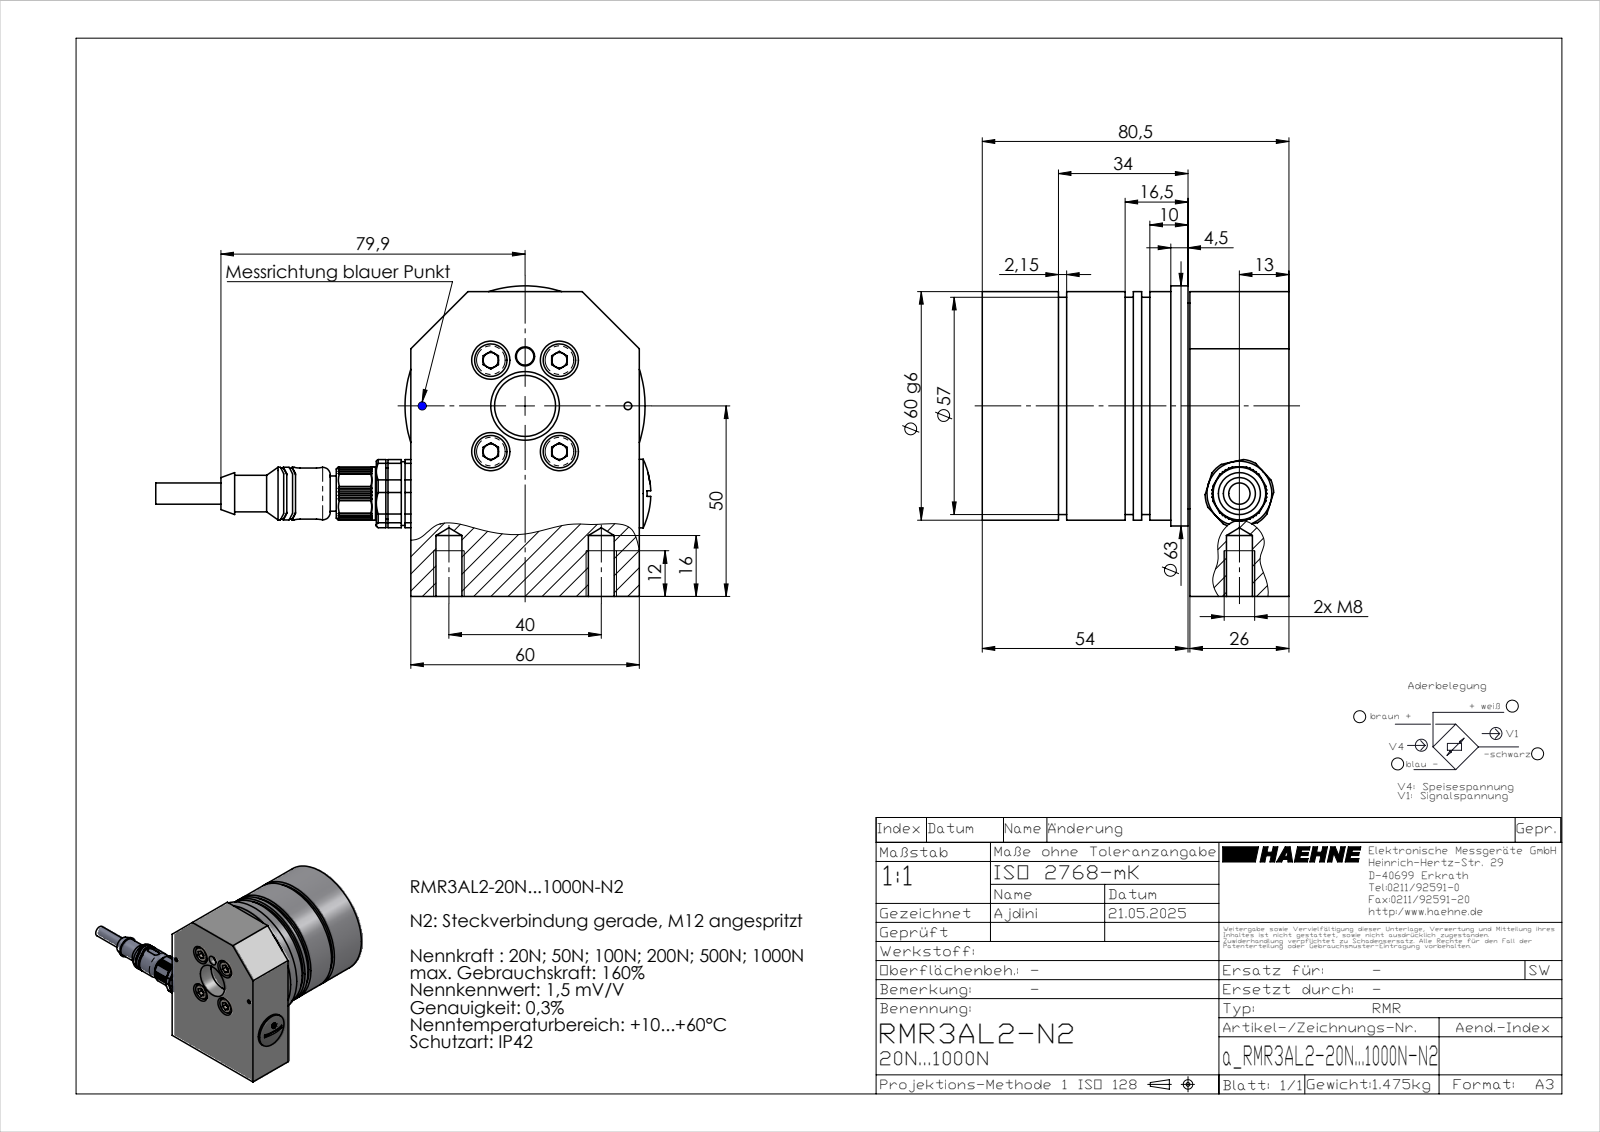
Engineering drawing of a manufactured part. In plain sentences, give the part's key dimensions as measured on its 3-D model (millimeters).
The part is named "a_RMR3AL2-20N...1000N-N2". Its 3-D file was written by "SolidWorks 2023 (AUTOMOTIVE_DESIGN)". It is 15 solids with 917 faces: 518 planar, 253 cylindrical and 146 other. Overall it measures 129.92 by 81.5 by 80.5 millimeters. Its volume is 235 095 cubic millimeters and its surface area 73 304 square millimeters. Round holes: 4 of diameter 1.1, 4 of diameter 1.15, 4 of diameter 1.6, 4 of diameter 1.85, 4 of diameter 4.2, 4 of diameter 5.3, 4 of diameter 10, 2 of diameter 2, 2 of diameter 6.8, 1 of diameter 0.64, 1 of diameter 1.2, 1 of diameter 3. Round bosses or shafts: 5 of diameter 0.86, 4 of diameter 8.5, 4 of diameter 5, 4 of diameter 1.8, 4 of diameter 1.55, 4 of diameter 1.5, 4 of diameter 1, 1 of diameter 63. Partial cylindrical surfaces (rounded edges, fillets, slot ends): 16 of radius 0.2, 9 of radius 0.3, 4 of radius 0.4, 4 of radius 0.53, 4 of radius 1, 4 of radius 1.27, 4 of radius 12, 2 of radius 1.6. The main face-to-face distances are 11.5, 48.5, 37, 73, 54.5, 62, 11, 47, 15, 26. The hole center spacings are 2.5, 3.54, 15, 21.63, 37.95, 5, 9.06, 18.
